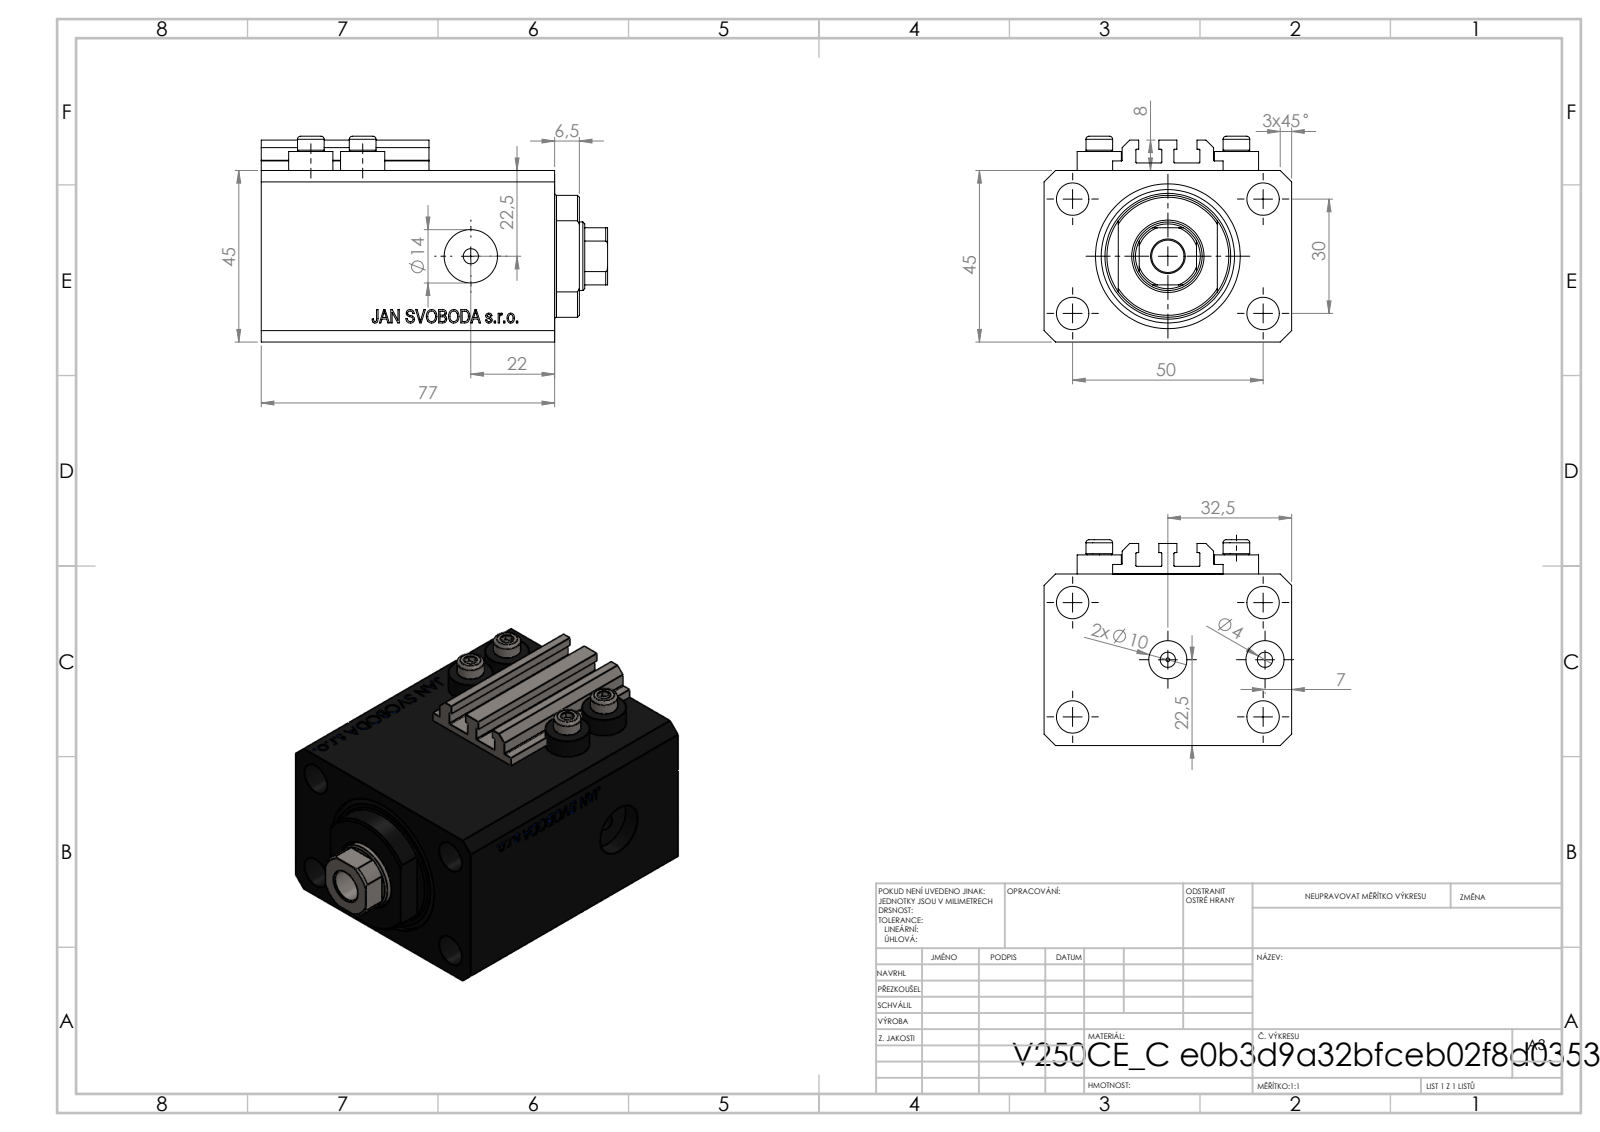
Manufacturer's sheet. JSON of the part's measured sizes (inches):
{"part_name": "V250CE_VC_C; V250CE_C_VCP; V250CE_C_Body; ALLEN BOLT V250CE", "step_written_by": "SolidWorks 2019 (CONFIG_CONTROL_DESIGN)", "units": "inches", "bodies": {"solids": 8, "faces": 1042, "planar": 504, "cylindrical": 92, "other": 446}, "overall_size": [3.583, 2.559, 2.126], "volume_in3": 12.91, "surface_area_in2": 89.4, "round_holes": [[0.157, 8], [0.335, 5], [0.394, 2], [0.551, 2], [0.049, 1], [0.709, 1], [0.984, 1], [1.496, 1]], "round_bosses_or_shafts": [[0.457, 4], [0.276, 4]], "partial_cylinders_radius": [[0.008, 10], [0.335, 1], [0.63, 1]], "face_to_face_distances": [1.772, 2.559, 0.551, 3.031, 2.48, 0.272, 2.209, 2.76, 0.118, 1.85], "hole_center_spacings": [1.148, 0.535, 0.591, 1.181, 1.417, 1.515, 1.969, 2.074]}
